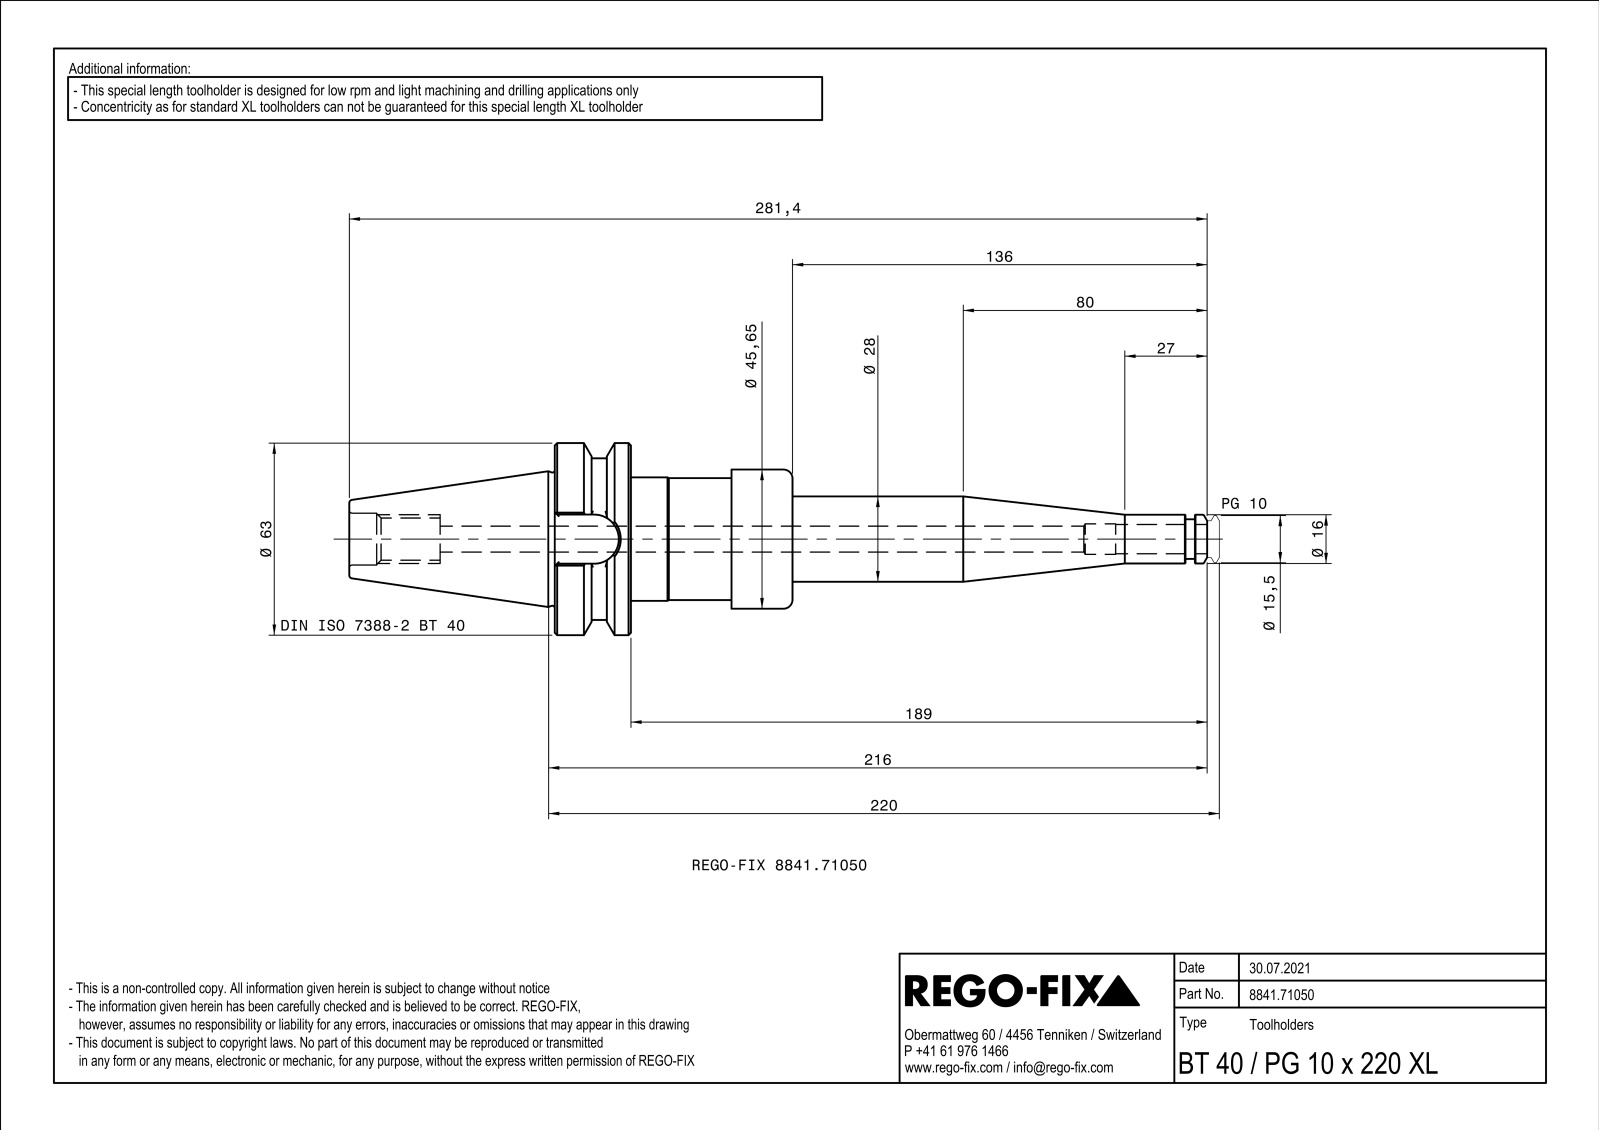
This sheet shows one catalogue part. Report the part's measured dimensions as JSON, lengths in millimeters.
{"part_name": "NOCUT", "step_written_by": "SIEMENS PLM Software Solid Edge ST10 (AUTOMOTIVE_DESIGN)", "units": "millimeters", "bodies": {"solids": 1, "faces": 149, "planar": 52, "cylindrical": 34, "other": 63}, "overall_size": [281.4, 63, 63], "volume_mm3": 233327, "surface_area_mm2": 52469, "round_holes": [[9, 1], [10, 1], [13.84, 1], [17, 1], [25, 1], [29, 1], [38.38, 1], [40.05, 1], [43.3, 1]], "round_bosses_or_shafts": [[63, 1], [53, 1], [45.65, 1], [40.5, 1], [40, 1], [34, 1], [33, 1], [28, 1]], "partial_cylinders_radius": [[0.5, 4], [8.05, 1], [22.77, 1]], "face_to_face_distances": [25, 53, 78, 6, 14, 1.5, 51.5, 76.5, 20, 18.5]}
